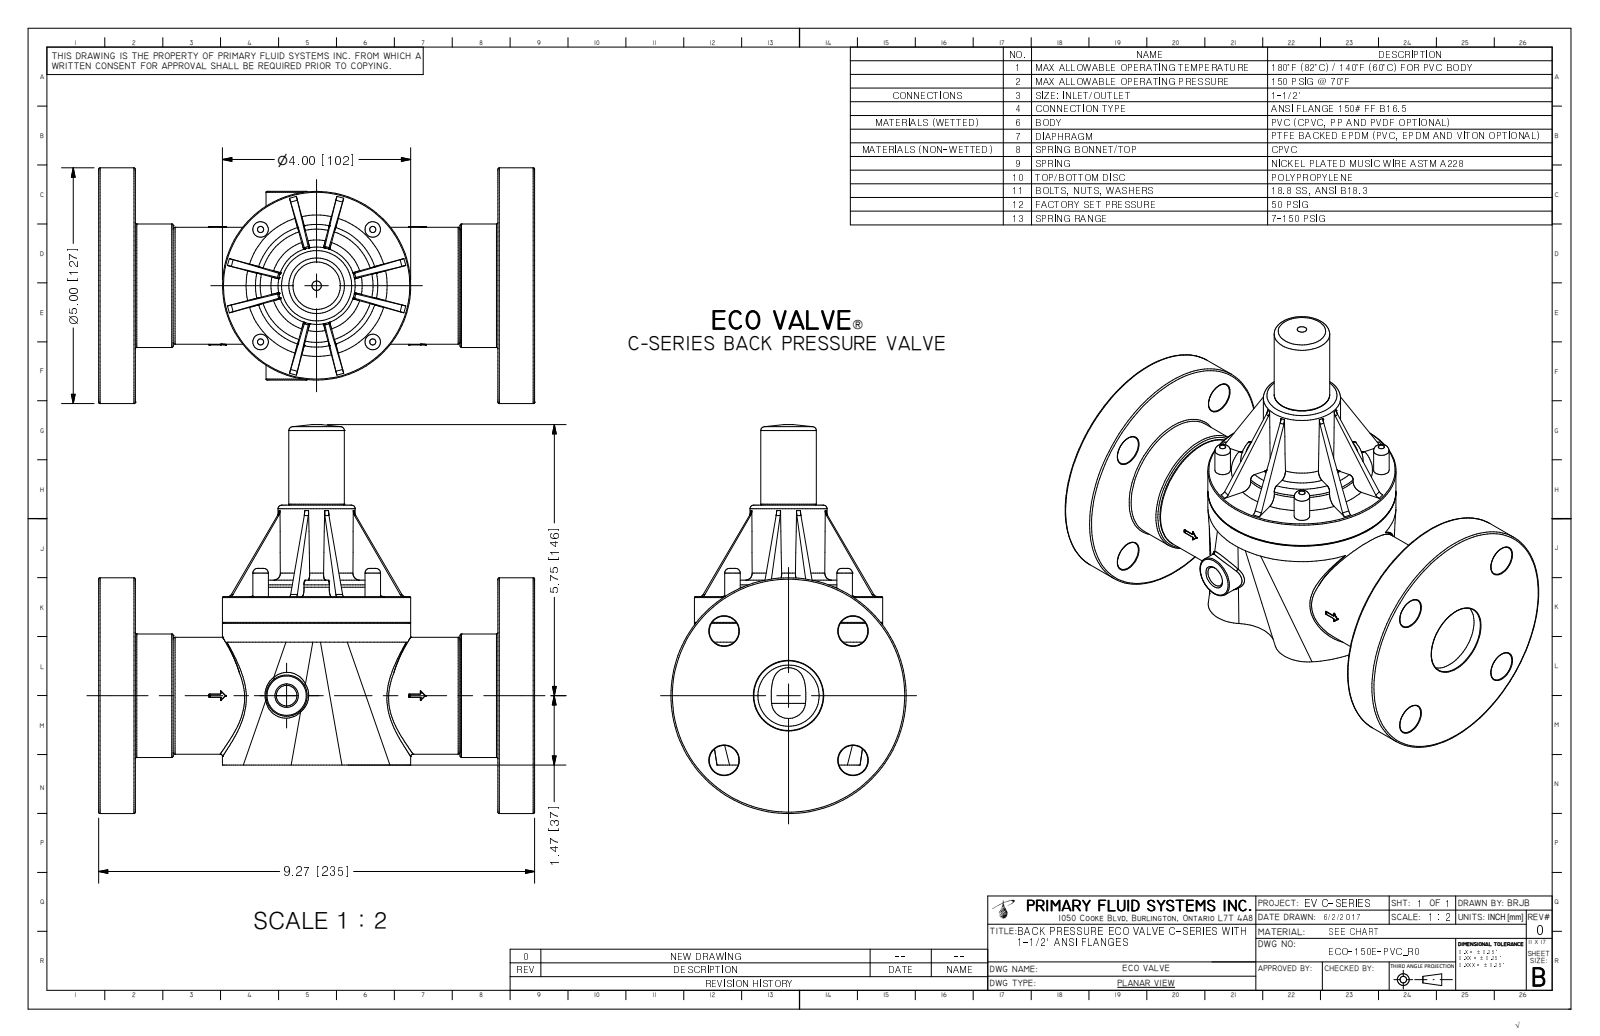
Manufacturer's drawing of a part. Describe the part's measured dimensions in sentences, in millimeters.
The part is named "ECO-150E-PVC_R0". Its 3-D file was written by "Autodesk Inventor 2009 (AUTOMOTIVE_DESIGN)". It is 1 solid with 450 faces: 171 planar, 95 cylindrical and 184 other. Overall it measures 235.5 by 209.5 by 127 millimeters. Its volume is 1 379 000 cubic millimeters and its surface area 207 300 square millimeters. Round holes: 4 of diameter 5.8, 4 of diameter 16, 1 of diameter 11.1, 1 of diameter 37.5, 1 of diameter 38.1. Round bosses or shafts: 4 of diameter 10.2, 4 of diameter 8.4, 1 of diameter 127, 1 of diameter 101.6, 1 of diameter 66.5, 1 of diameter 66, 1 of diameter 63, 1 of diameter 48.3. Partial cylindrical surfaces (rounded edges, fillets, slot ends): 14 of radius 2.5, 4 of radius 1.3, 4 of radius 5.7, 1 of radius 3.8, 1 of radius 22.2, 1 of radius 31.8, 1 of radius 37.4, 1 of radius 39.6. The main face-to-face distances are 19.8, 215.6, 235.5, 195.8, 90.7, 40.3, 195.2, 20.4, 175.4, 73.8. The hole center spacings are 49.2, 60.6, 69.6, 69.6, 85.7, 98.4.
